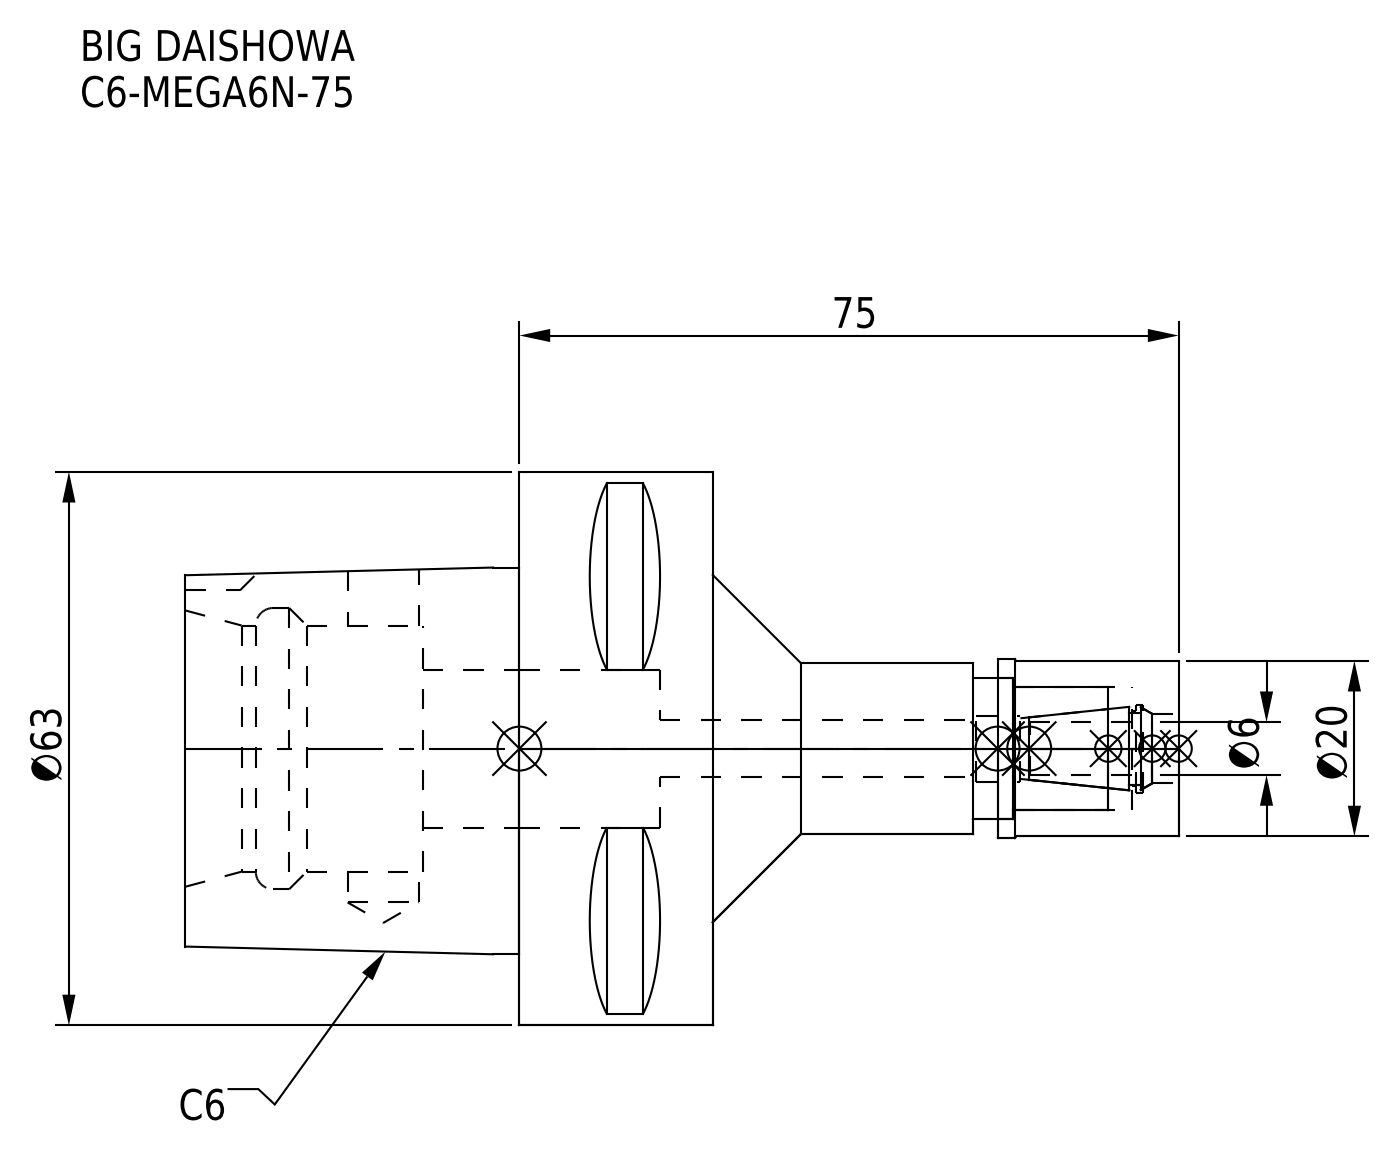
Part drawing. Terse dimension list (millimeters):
name: DXF_TEMP_ASSY_ASM_4_ASM.stp; MGN6_1.stp; C6-MEGA6N-75-060-FreeParts; C6-MEGA6N-75_1.stp (+3 more)
written by: SolidWorks 2019 (CONFIG_CONTROL_DESIGN)
unit: mm
bodies: 2 solids, 95 faces (38 planar, 39 cylindrical, 18 other)
size: 113 × 63 × 63
volume: 113 984 mm³; area: 26 147 mm²
holes: 1× ⌀6.4, 1× ⌀7.5, 1× ⌀7.9, 1× ⌀8.1, 1× ⌀8.5, 1× ⌀10, 1× ⌀14, 1× ⌀16, 1× ⌀18, 1× ⌀28, 1× ⌀32
bosses: 1× ⌀63, 1× ⌀20.3, 1× ⌀20, 1× ⌀19.5
rounds: 1× R5
face distances: 22, 27, 60, 38, 33, 11, 53, 75, 86, 113
